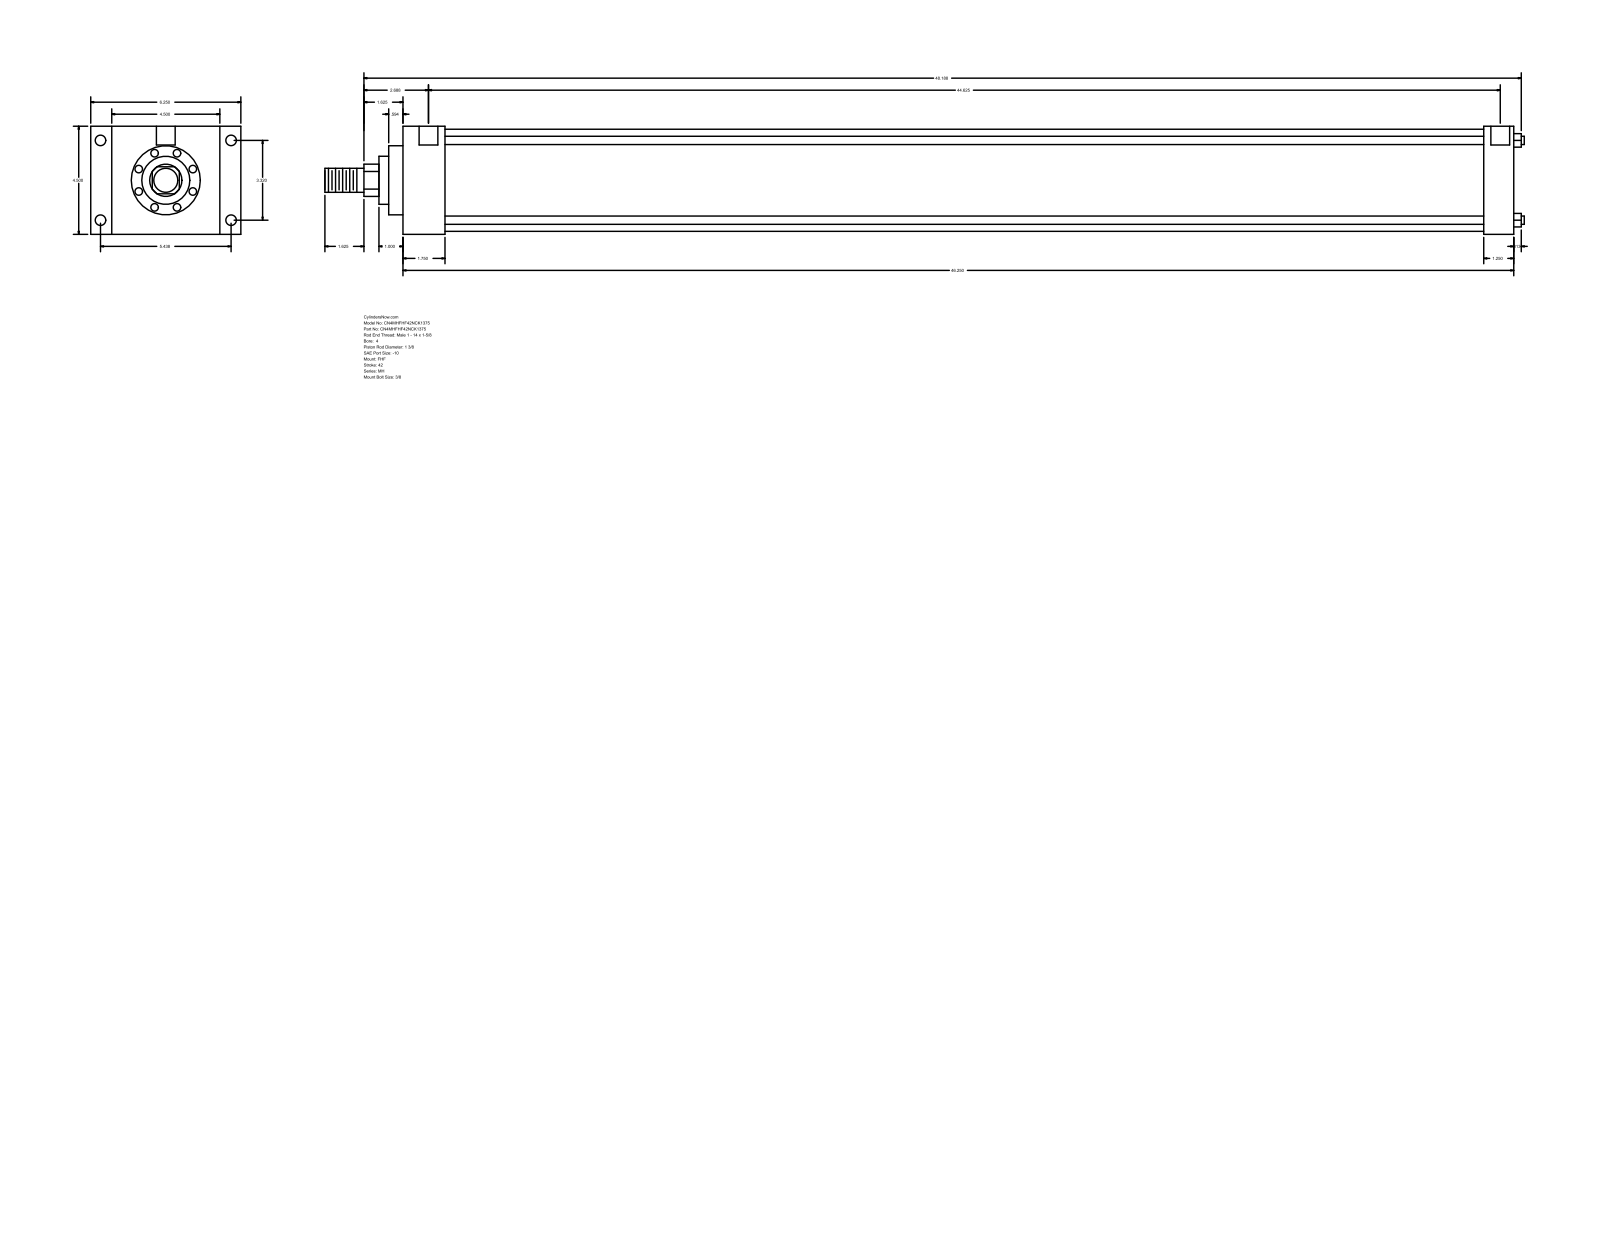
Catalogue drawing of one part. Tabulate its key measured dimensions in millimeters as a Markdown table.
| quantity | value |
| --- | --- |
| part name | MH_FHF__0400_1.375 |
| STEP written by | GSSL Pune (CONFIG_CONTROL_DESIGN) |
| units | millimeters |
| bodies | 0 solids, 90 faces (61 planar, 29 cylindrical, 0 other) |
| overall size | 1268.41 × 158.75 × 114.3 |
| round holes (diameter × count) | 8.73 × 4, 11.13 × 4, 19.84 × 2 |
| round bosses / shafts (diameter × count) | 8.76 × 4, 107.95 × 1, 73.03 × 1, 50.8 × 1, 34.92 × 1, 25.4 × 1 |
| partial cylindrical surfaces (radius × count) | 17.06 × 1 |
| main face-to-face distances | 114.3, 1174.76, 44.45, 1130.31, 22.23, 136.53, 158.76, 1143.01, 1098.56, 31.75 |
| hole center spacings | 1.59, 84.32, 138.12, 161.82, 1135.07, 1136.66, 1133.48 |
